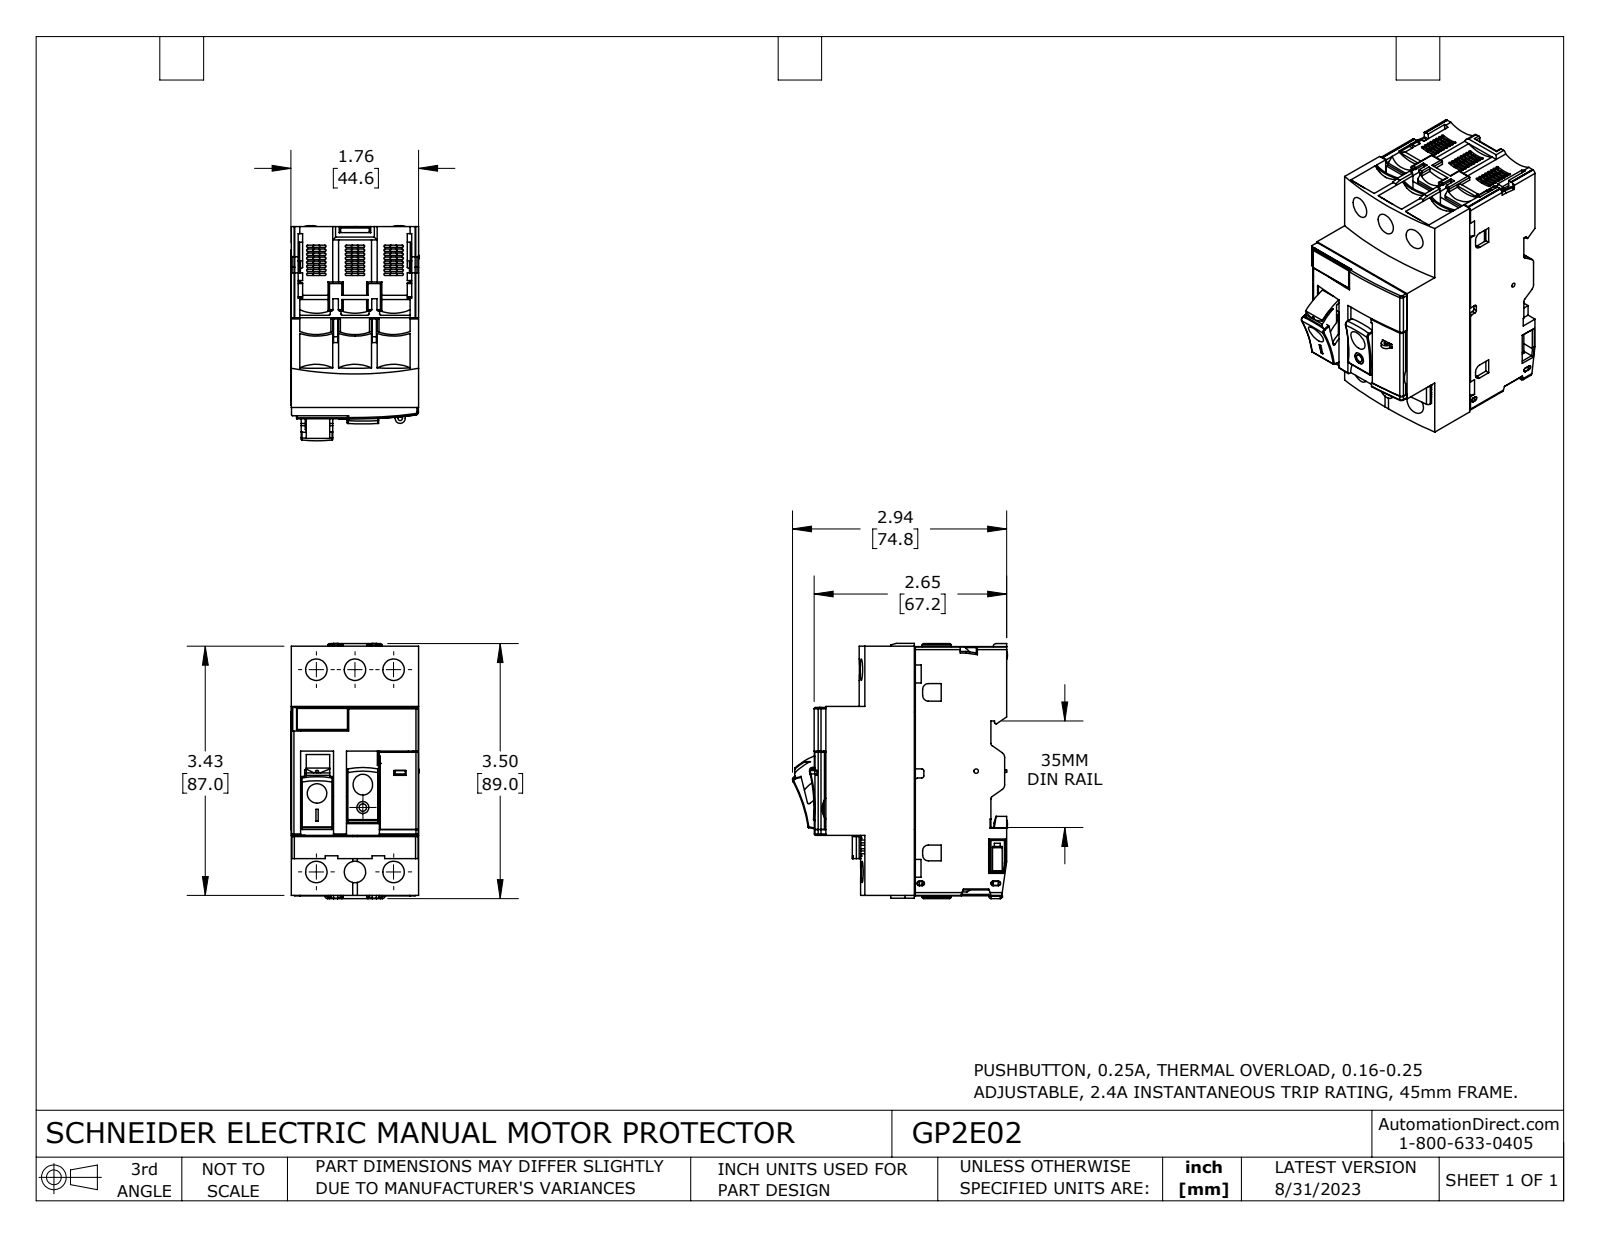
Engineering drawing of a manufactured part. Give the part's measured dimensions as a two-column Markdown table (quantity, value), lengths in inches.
| quantity | value |
| --- | --- |
| part name | GP2E02 |
| STEP written by | SolidWorks 2021 (CONFIG_CONTROL_DESIGN) |
| units | inches |
| bodies | 15 solids, 2269 faces (1521 planar, 657 cylindrical, 91 other) |
| overall size | 3.508 × 2.957 × 1.764 |
| volume | 11.58 in³ |
| surface area | 98.93 in² |
| round holes (diameter × count) | 0.295 × 6, 0.197 × 5, 0.059 × 2, 0.157 × 1, 0.165 × 1, 0.315 × 1, 0.327 × 1, 0.335 × 1, 0.343 × 1 |
| round bosses / shafts (diameter × count) | 0.244 × 2, 0.118 × 2, 0.382 × 1, 0.102 × 1, 0.047 × 1 |
| partial cylindrical surfaces (radius × count) | 0.016 × 104, 0.02 × 47, 0.039 × 16, 0.01 × 12, 0.012 × 12, 0.031 × 12, 0.059 × 8, 0.004 × 6 |
| main face-to-face distances | 1.752, 0.531, 0.115, 1.233, 1.756, 0.059, 1.637, 0.581, 1.053, 1.171 |
| hole center spacings | 0.531, 2.83, 2.779, 0.346, 0.402, 0.546, 0.671, 0.726 |
